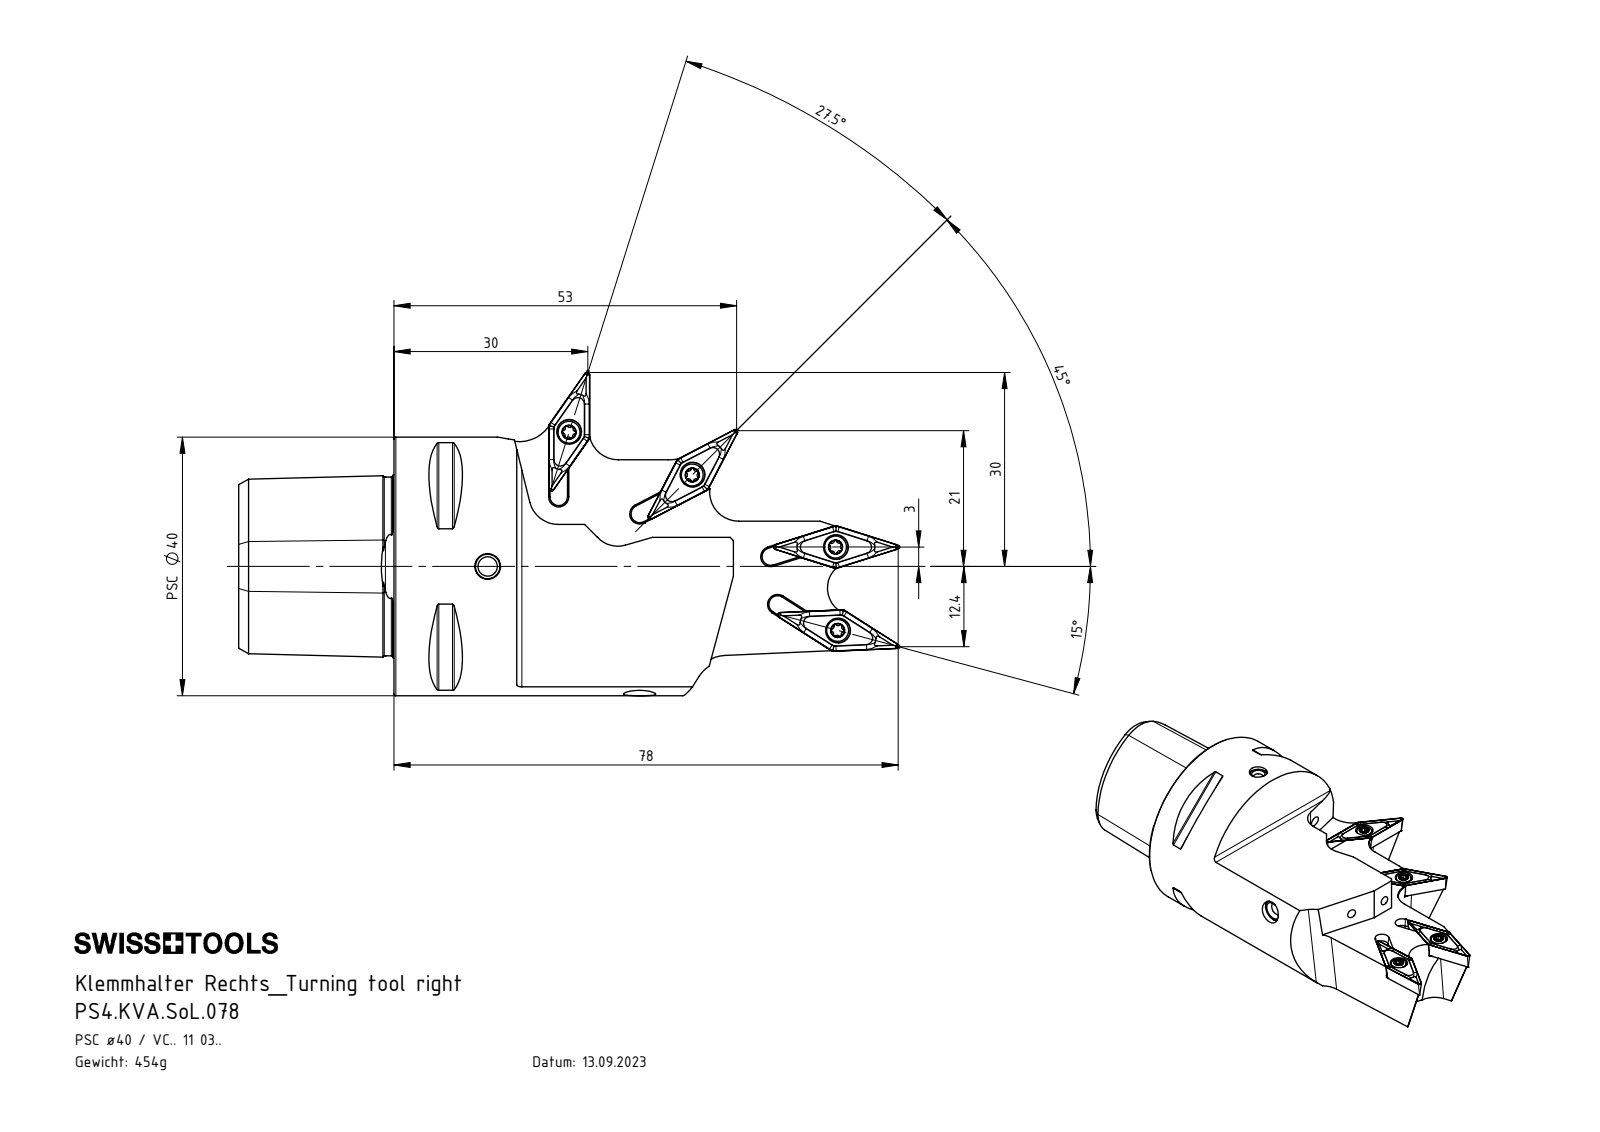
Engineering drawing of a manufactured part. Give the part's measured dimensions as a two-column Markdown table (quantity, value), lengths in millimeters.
| quantity | value |
| --- | --- |
| part name | KVT_MB_600_040; KVT_MB_600_050; WCA-ER2.001.006_A; PS4.KVA.SoL.078 (+2 more) |
| STEP written by | SolidWorks 2017 (AUTOMOTIVE_DESIGN) |
| units | millimeters |
| bodies | 13 solids, 664 faces (167 planar, 177 cylindrical, 320 other) |
| overall size | 102.01 × 50.02 × 40 |
| volume | 57 314 mm³ |
| surface area | 17 124 mm² |
| round holes (diameter × count) | 2 × 4, 2.05 × 4, 2.8 × 4, 3.85 × 4, 4 × 2, 3 × 1, 3.3 × 1, 4.2 × 1, 4.6 × 1, 5 × 1, 12.5 × 1, 18 × 1 |
| round bosses / shafts (diameter × count) | 3.4 × 4, 2.5 × 4, 40 × 1, 5 × 1, 4 × 1 |
| partial cylindrical surfaces (radius × count) | 0.21 × 24, 0.36 × 16, 0.3 × 8, 0.36 × 8, 4.5 × 5, 1.35 × 4, 0.8 × 2, 4.25 × 2 |
| main face-to-face distances | 22.3, 15, 7.3, 11.82, 3.18, 10.48, 19, 24, 43, 15.52 |
| hole center spacings | 12.89, 32.92, 32.98, 2.5, 12.91, 12.92, 20.17, 20.18 |
